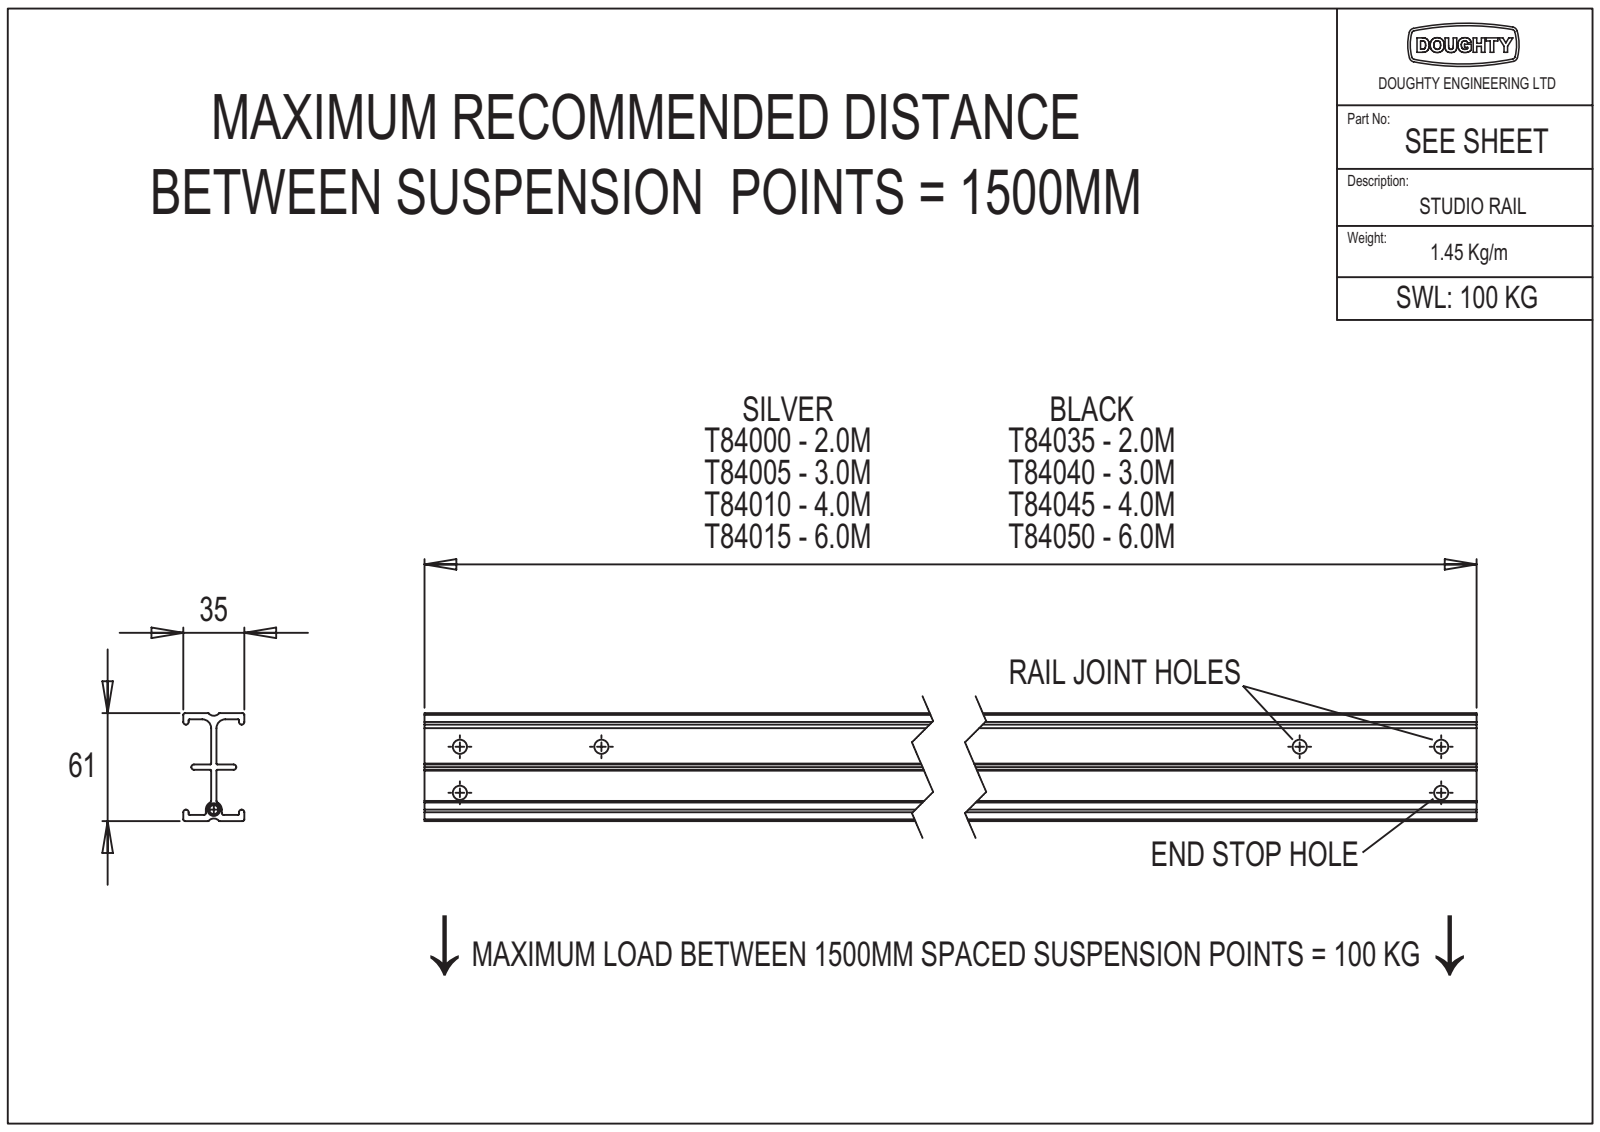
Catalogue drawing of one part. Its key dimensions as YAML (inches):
part_name: "T84000"
step_written_by: "SolidWorks 2016 (CONFIG_CONTROL_DESIGN)"
units: inches
bodies: {solids: 1, faces: 438, planar: 300, cylindrical: 56, other: 82}
overall_size: [78.74, 2.402, 1.358]
volume: 62.79
surface_area: 995.7
round_holes:
  - {diameter: 0.315, count: 6}
  - {diameter: 0.203, count: 1}
partial_cylinders:
  - {radius: 0.02, count: 12}
  - {radius: 0.039, count: 12}
  - {radius: 0.059, count: 6}
  - {radius: 0.148, count: 2}
  - {radius: 0.197, count: 2}
  - {radius: 0.177, count: 1}
face_to_face_distances: [0.118, 1.142, 1.26, 1.122, 0.138, 2.264, 1.004, 2.402, 0.62, 0.738]
hole_center_spacings: [0.866, 3.15, 3.267, 74.016, 74.021, 77.165, 77.17, 70.866]
